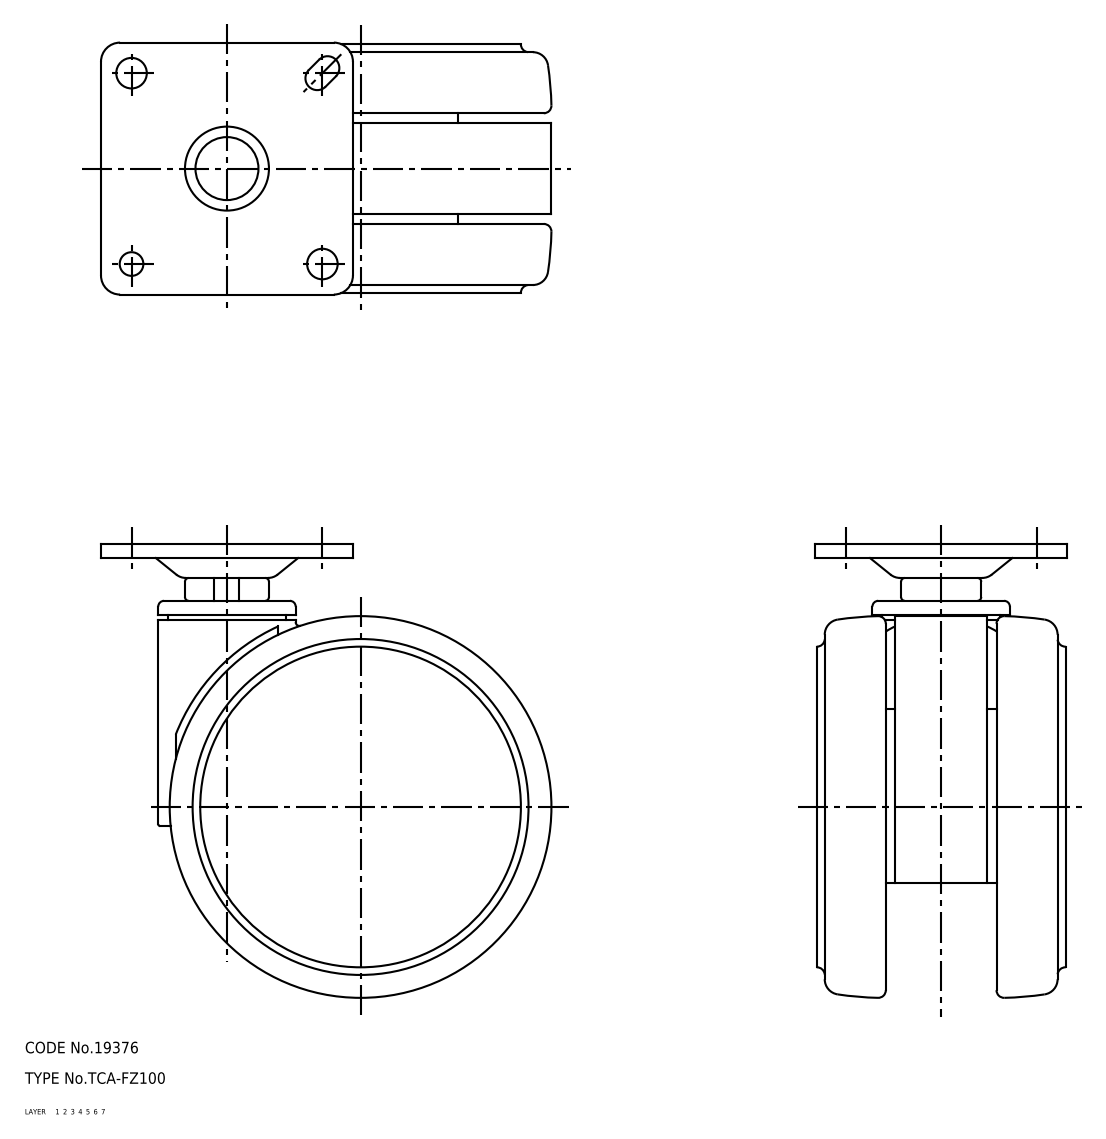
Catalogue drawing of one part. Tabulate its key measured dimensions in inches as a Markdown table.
| quantity | value |
| --- | --- |
| part name | caster; TCA-FZ100 |
| STEP written by | SolidWorks 2015 (AUTOMOTIVE_DESIGN) |
| units | inches |
| bodies | 1 solid, 2377 faces (801 planar, 1098 cylindrical, 478 other) |
| overall size | 4.685 × 4.646 × 2.598 |
| volume | 18.98 in³ |
| surface area | 204 in² |
| round holes (diameter × count) | 0.315 × 2, 0.244 × 1, 0.358 × 1, 0.394 × 1, 0.398 × 1, 0.413 × 1, 0.472 × 1, 0.591 × 1, 0.598 × 1, 0.622 × 1, 0.756 × 1, 1.024 × 1 |
| round bosses / shafts (diameter × count) | 3.457 × 1, 1.417 × 1, 1.22 × 1, 1.098 × 1, 1.087 × 1, 0.866 × 1, 0.787 × 1, 0.748 × 1 |
| partial cylindrical surfaces (radius × count) | 0.02 × 200, 0.047 × 160, 0.039 × 81, 0.008 × 16, 0.079 × 13, 0.012 × 12, 0.059 × 8, 0.031 × 6 |
| main face-to-face distances | 0.071, 2.425, 2.496, 0.142, 2.354, 0.571, 0.642, 0.522, 0.713, 1.854 |
| hole center spacings | 1.392, 1.969, 2.784 |
